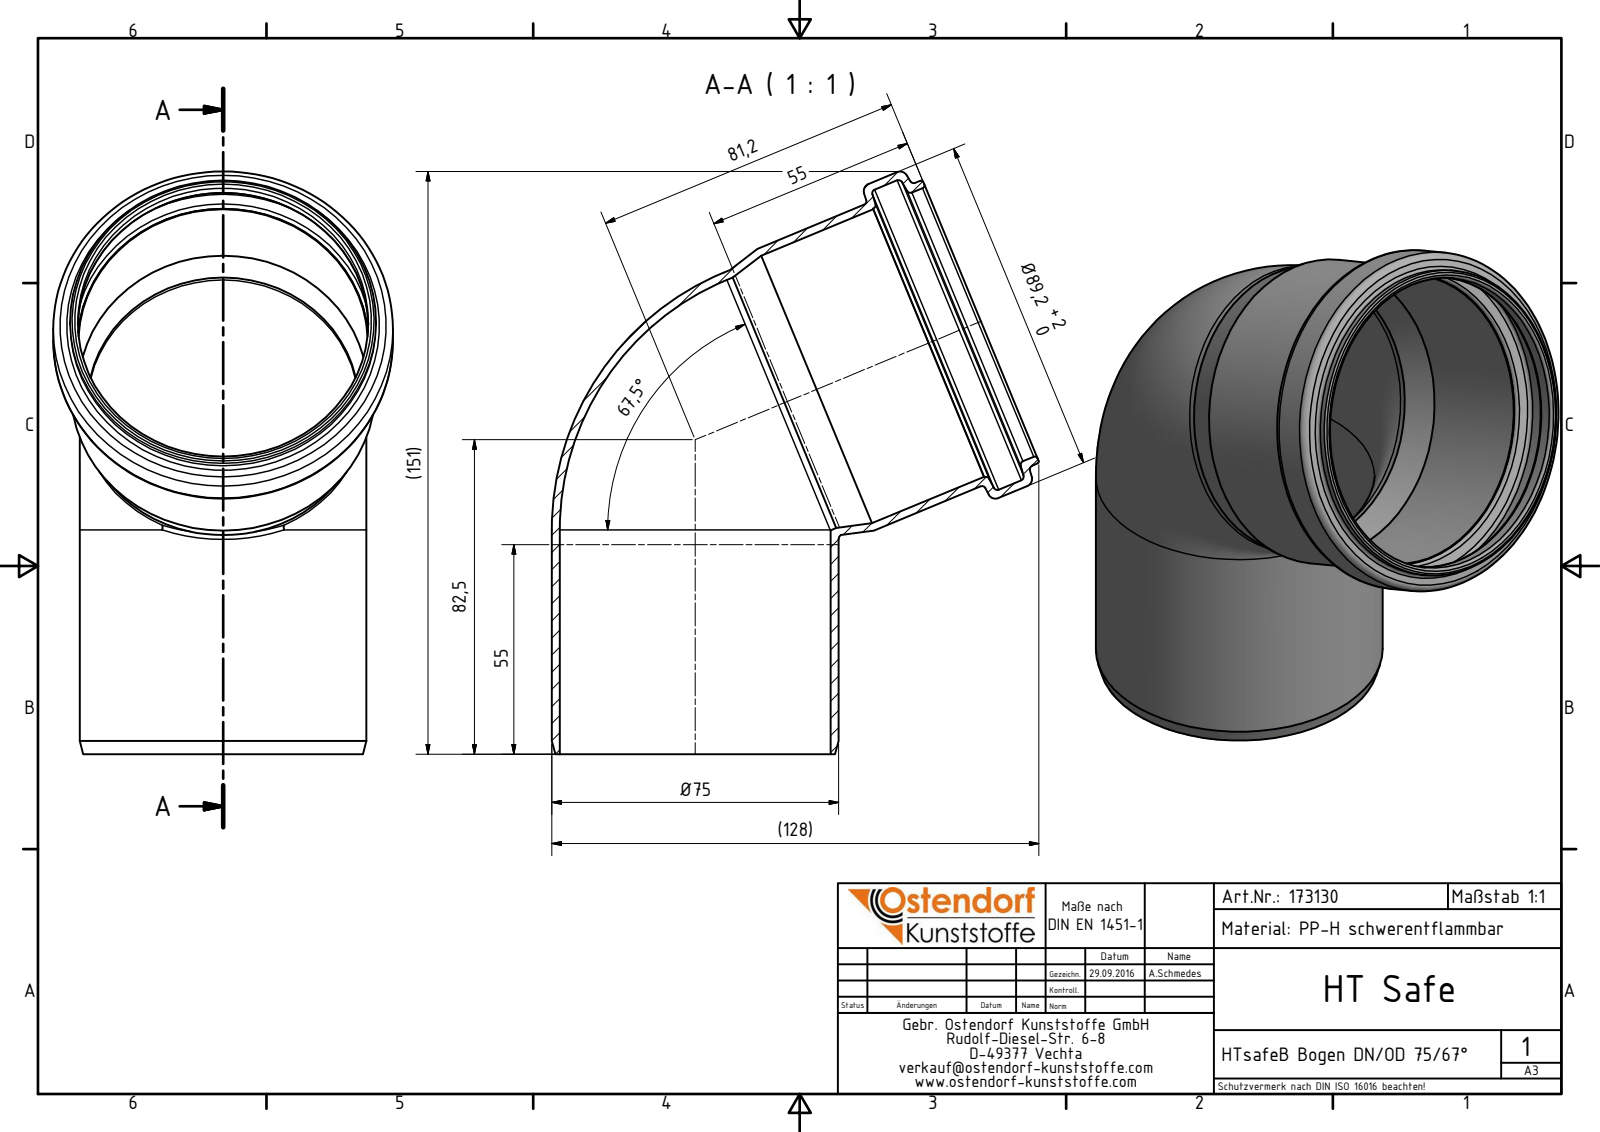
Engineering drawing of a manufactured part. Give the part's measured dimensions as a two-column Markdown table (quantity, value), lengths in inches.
| quantity | value |
| --- | --- |
| part name | 173130 HTsafeB DN_OD 75_67° |
| STEP written by | Autodesk Inventor 2016 (AUTOMOTIVE_DESIGN) |
| units | inches |
| bodies | 1 solid, 34 faces (3 planar, 11 cylindrical, 20 other) |
| overall size | 6.02 × 5.035 × 3.512 |
| volume | 4.568 in³ |
| surface area | 122.5 in² |
| round holes (diameter × count) | 2.799 × 2, 2.992 × 1, 3.004 × 1, 3.354 × 1 |
| round bosses / shafts (diameter × count) | 2.965 × 2, 3.512 × 1, 3.161 × 1, 3.15 × 1 |
| main face-to-face distances | 0.586 |
